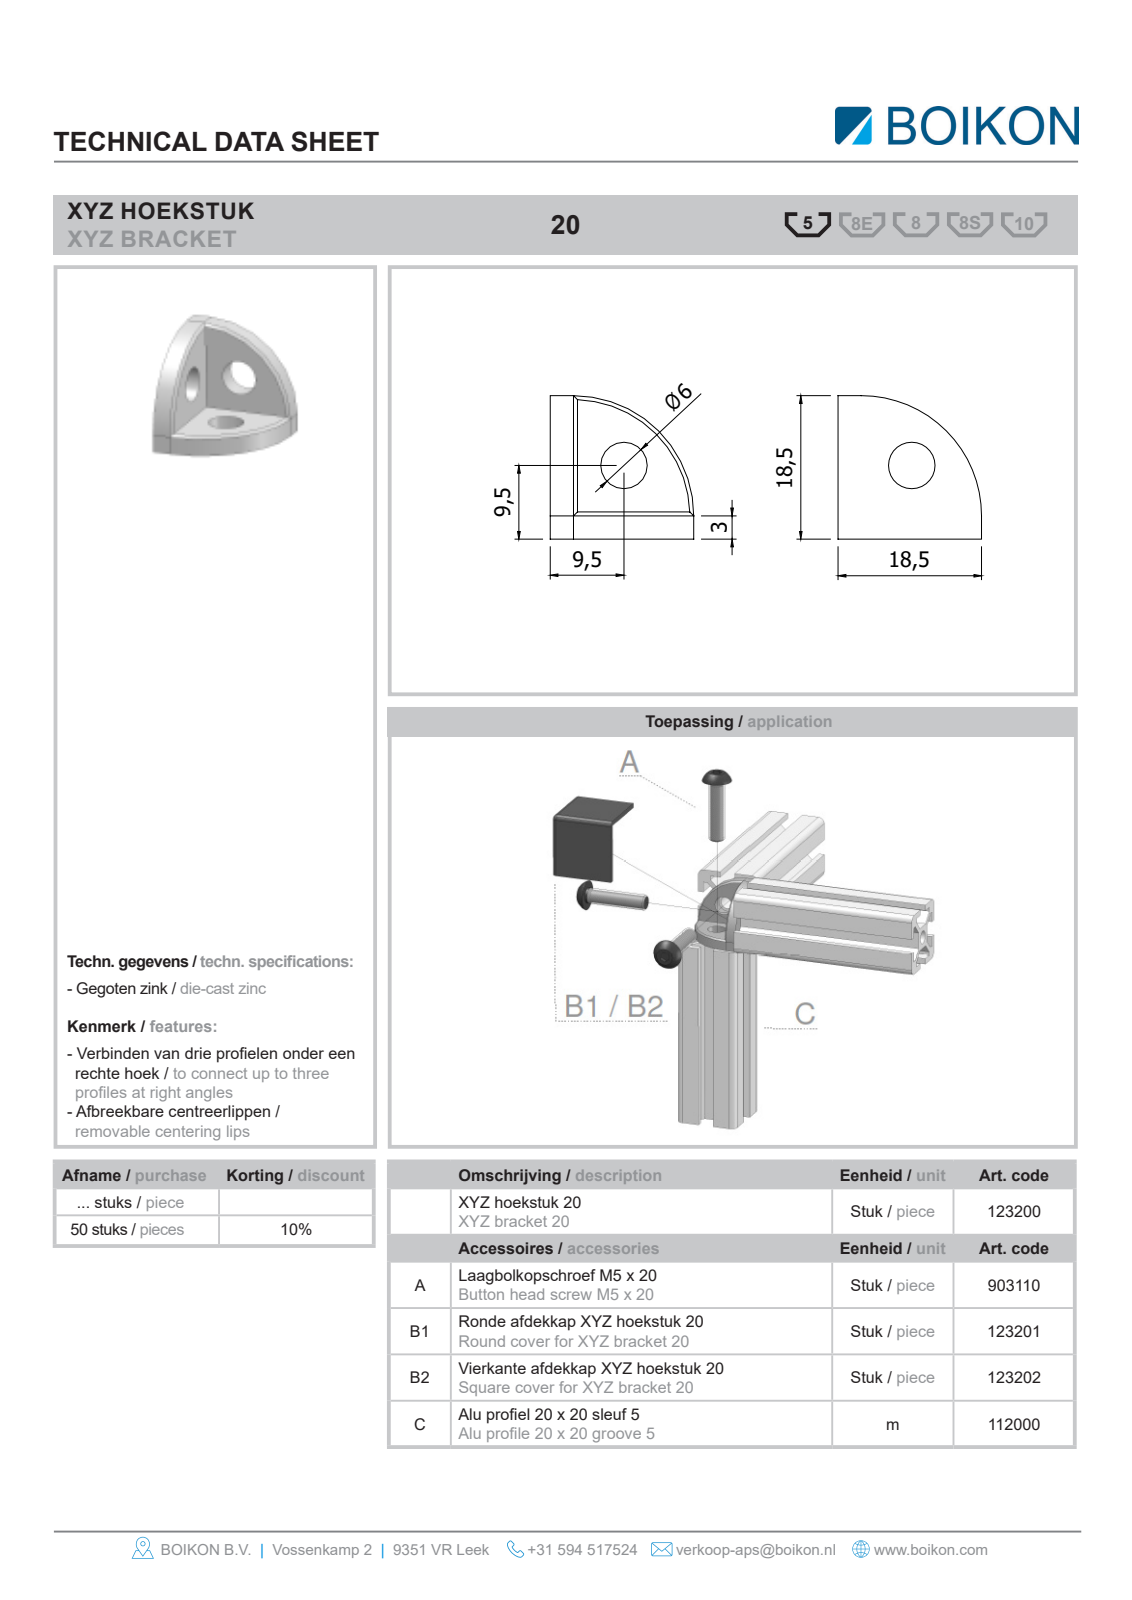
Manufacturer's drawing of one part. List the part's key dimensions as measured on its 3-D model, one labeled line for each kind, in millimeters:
Part name (STEP PRODUCT): Root; 123200XYZ HOEKSTUK 20BOIKON; 120015Laagbolkopschroef M5 x 20BOIKON0
STEP written by: HiCAD 2013 1802.4 Build 509 (AUTOMOTIVE_DESIGN)
Units: millimetres
Bodies: 4 solids, 60 faces (39 planar, 12 cylindrical, 9 other)
Overall size (bounding box): 35 × 35 × 35
Volume: 3 276 mm³ · Surface area: 3 021 mm²
Round holes (diameter × count): ⌀6 ×3
Round bosses / shafts (diameter × count): ⌀5 ×3, ⌀4.02 ×3
Partial cylindrical surfaces — rounded edges, fillets, slot ends (radius × count): R15.5 ×3
Main face-to-face distances: 3.5, 6.25, 2.75, 16.5, 20, 22.75, 35, 18.5, 15, 12.25
